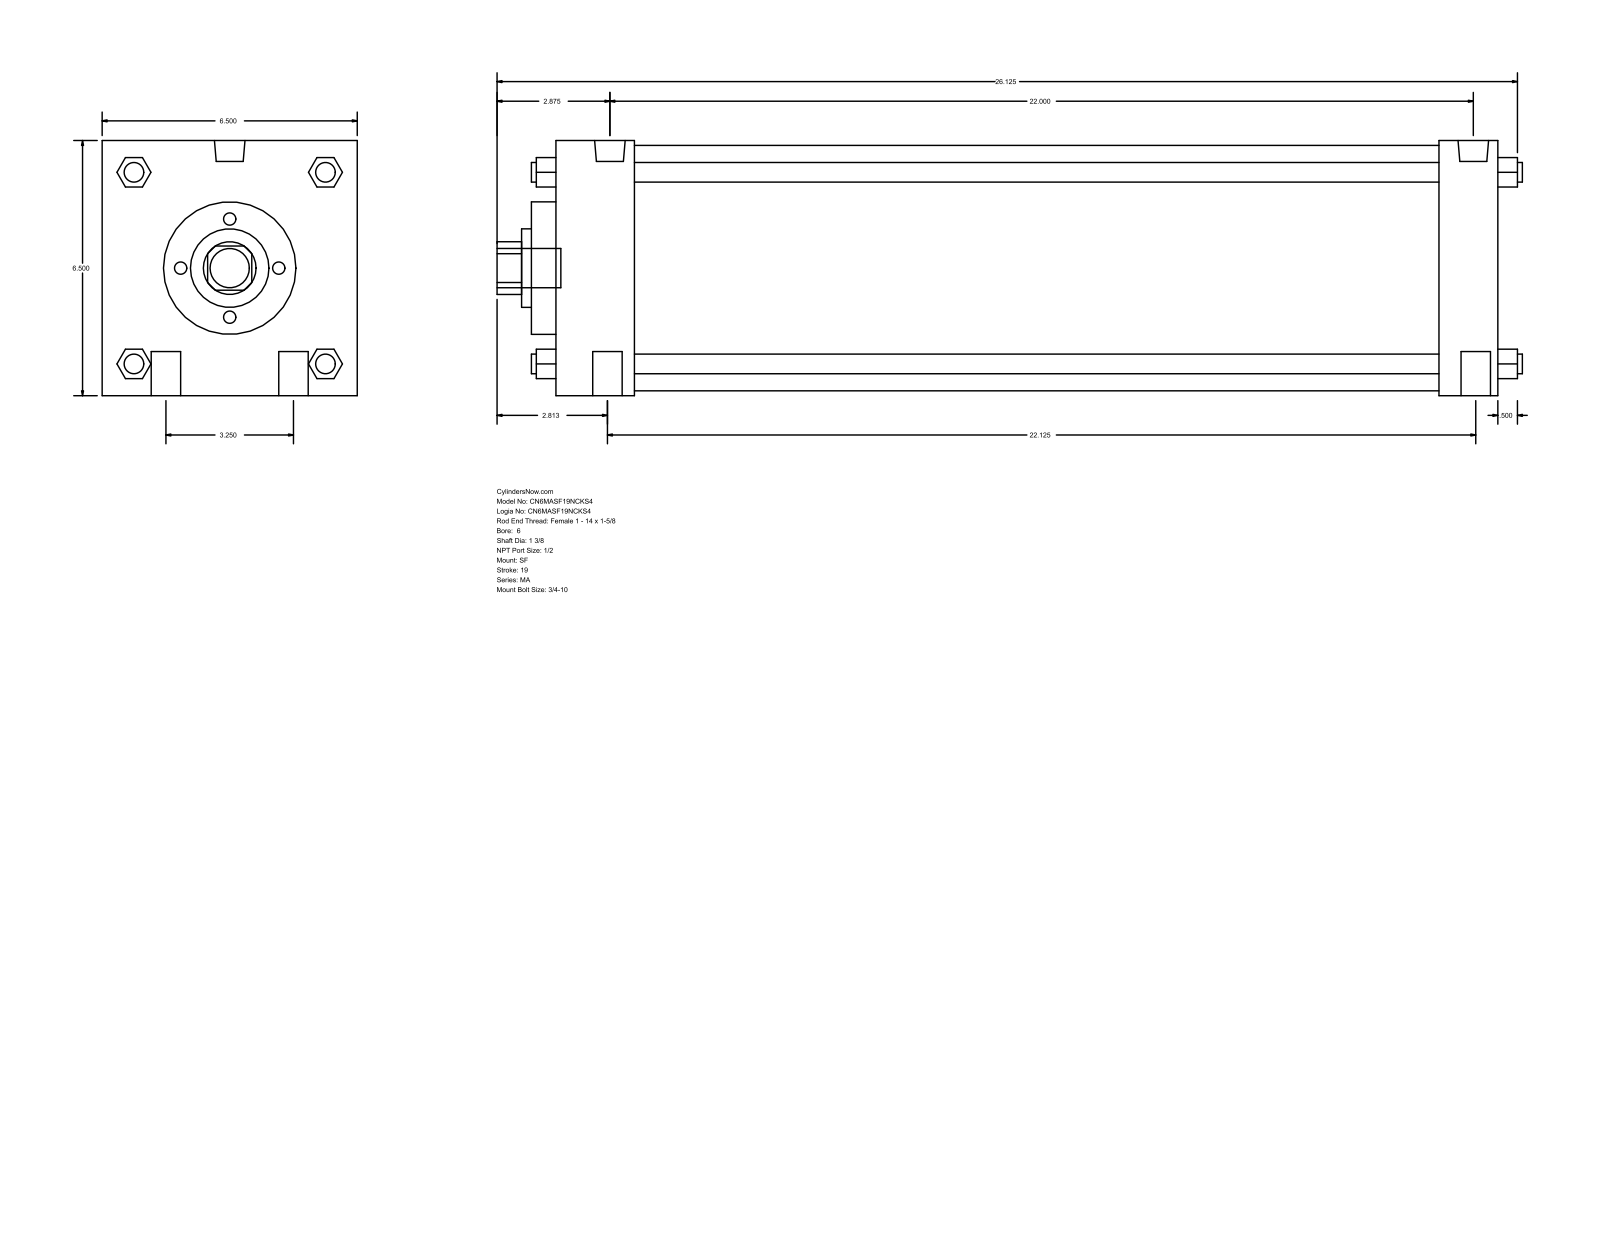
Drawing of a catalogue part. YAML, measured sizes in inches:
part_name: "MA_SF__0600_1.375"
step_written_by: "GSSL Pune (CONFIG_CONTROL_DESIGN)"
units: inches
bodies: {solids: 0, faces: 126, planar: 95, cylindrical: 31, other: 0}
overall_size: [26.125, 6.5, 6.5]
round_holes:
  - {diameter: 1.375, count: 1}
  - {diameter: 2, count: 1}
  - {diameter: 3.375, count: 1}
  - {diameter: 6.25, count: 1}
round_bosses_or_shafts:
  - {diameter: 0.75, count: 4}
  - {diameter: 0.5, count: 4}
  - {diameter: 0.778, count: 2}
  - {diameter: 0.687, count: 2}
  - {diameter: 1, count: 1}
partial_cylinders:
  - {radius: 0.672, count: 1}
face_to_face_distances: [6.5, 24, 22.5, 2, 1.5, 20.5, 22, 0.625, 2.625, 23.125]
